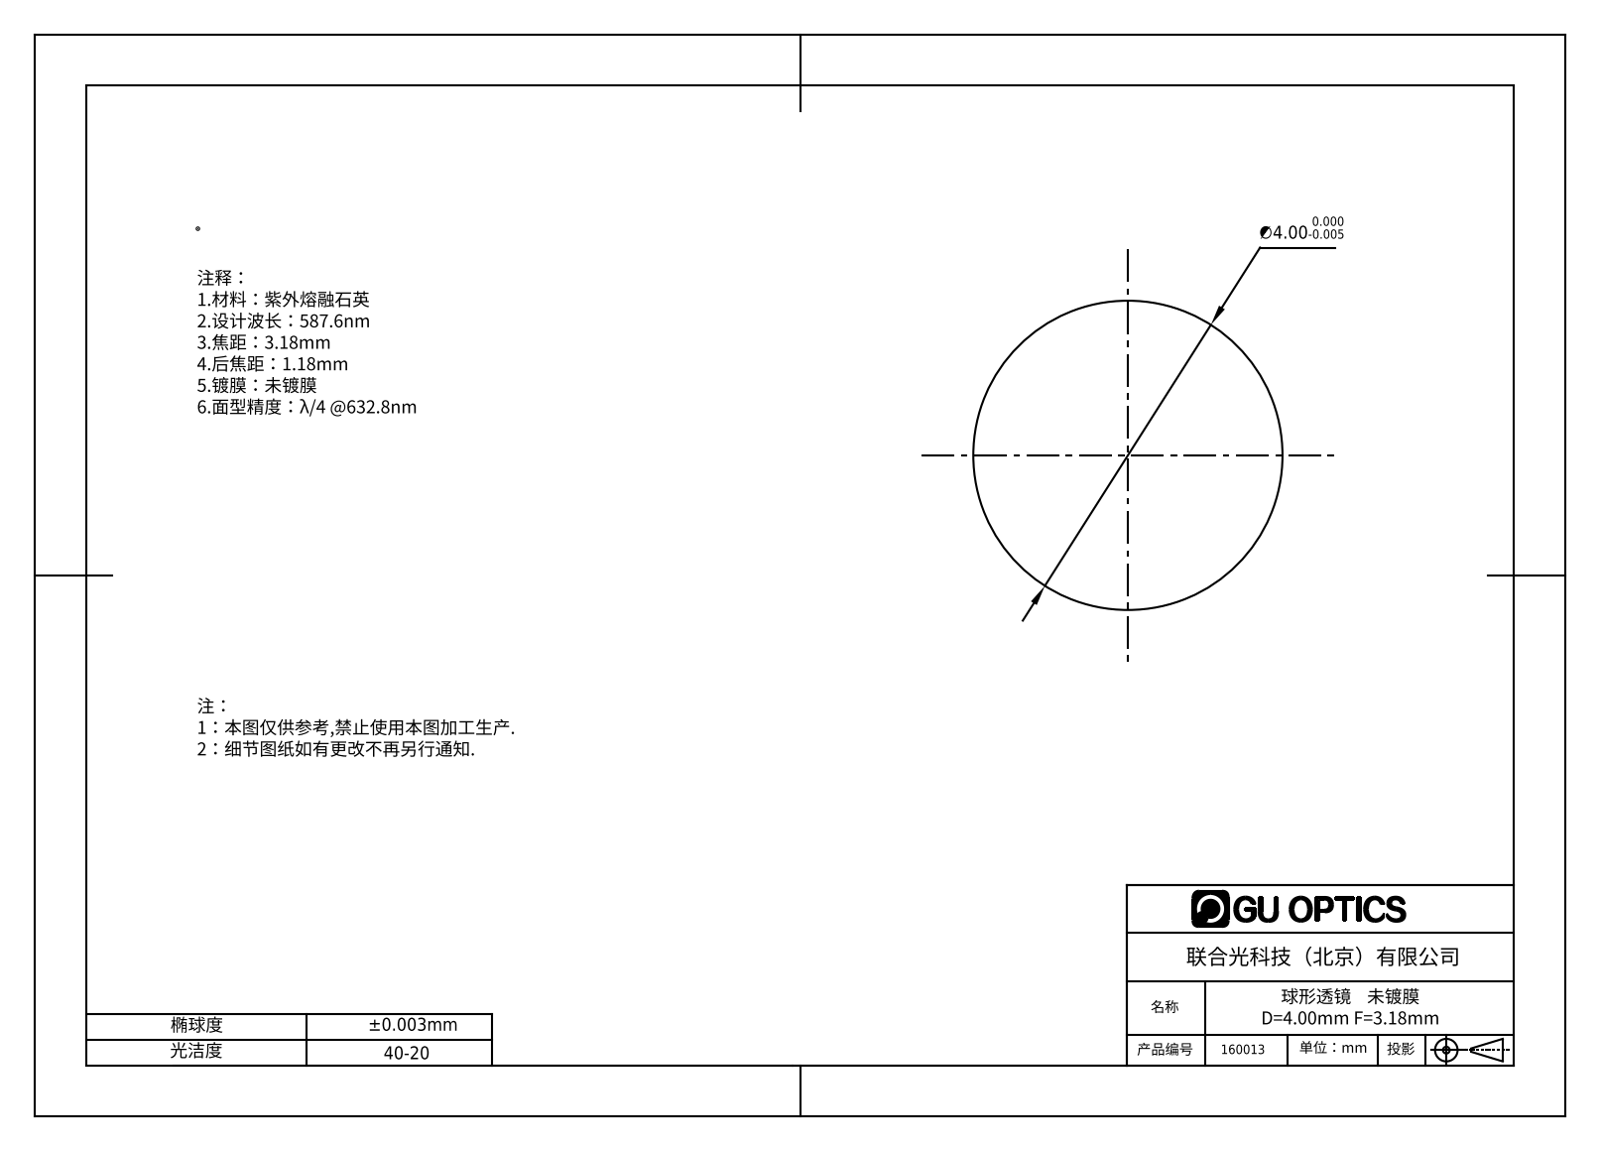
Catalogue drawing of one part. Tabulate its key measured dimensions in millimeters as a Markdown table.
| quantity | value |
| --- | --- |
| part name | 160003 |
| STEP written by | SolidWorks 2016 (CONFIG_CONTROL_DESIGN) |
| units | millimeters |
| bodies | 1 solid, 2 faces (0 planar, 0 cylindrical, 2 other) |
| overall size | 4 × 4 × 4 |
| volume | 34 mm³ |
| surface area | 50 mm² |
